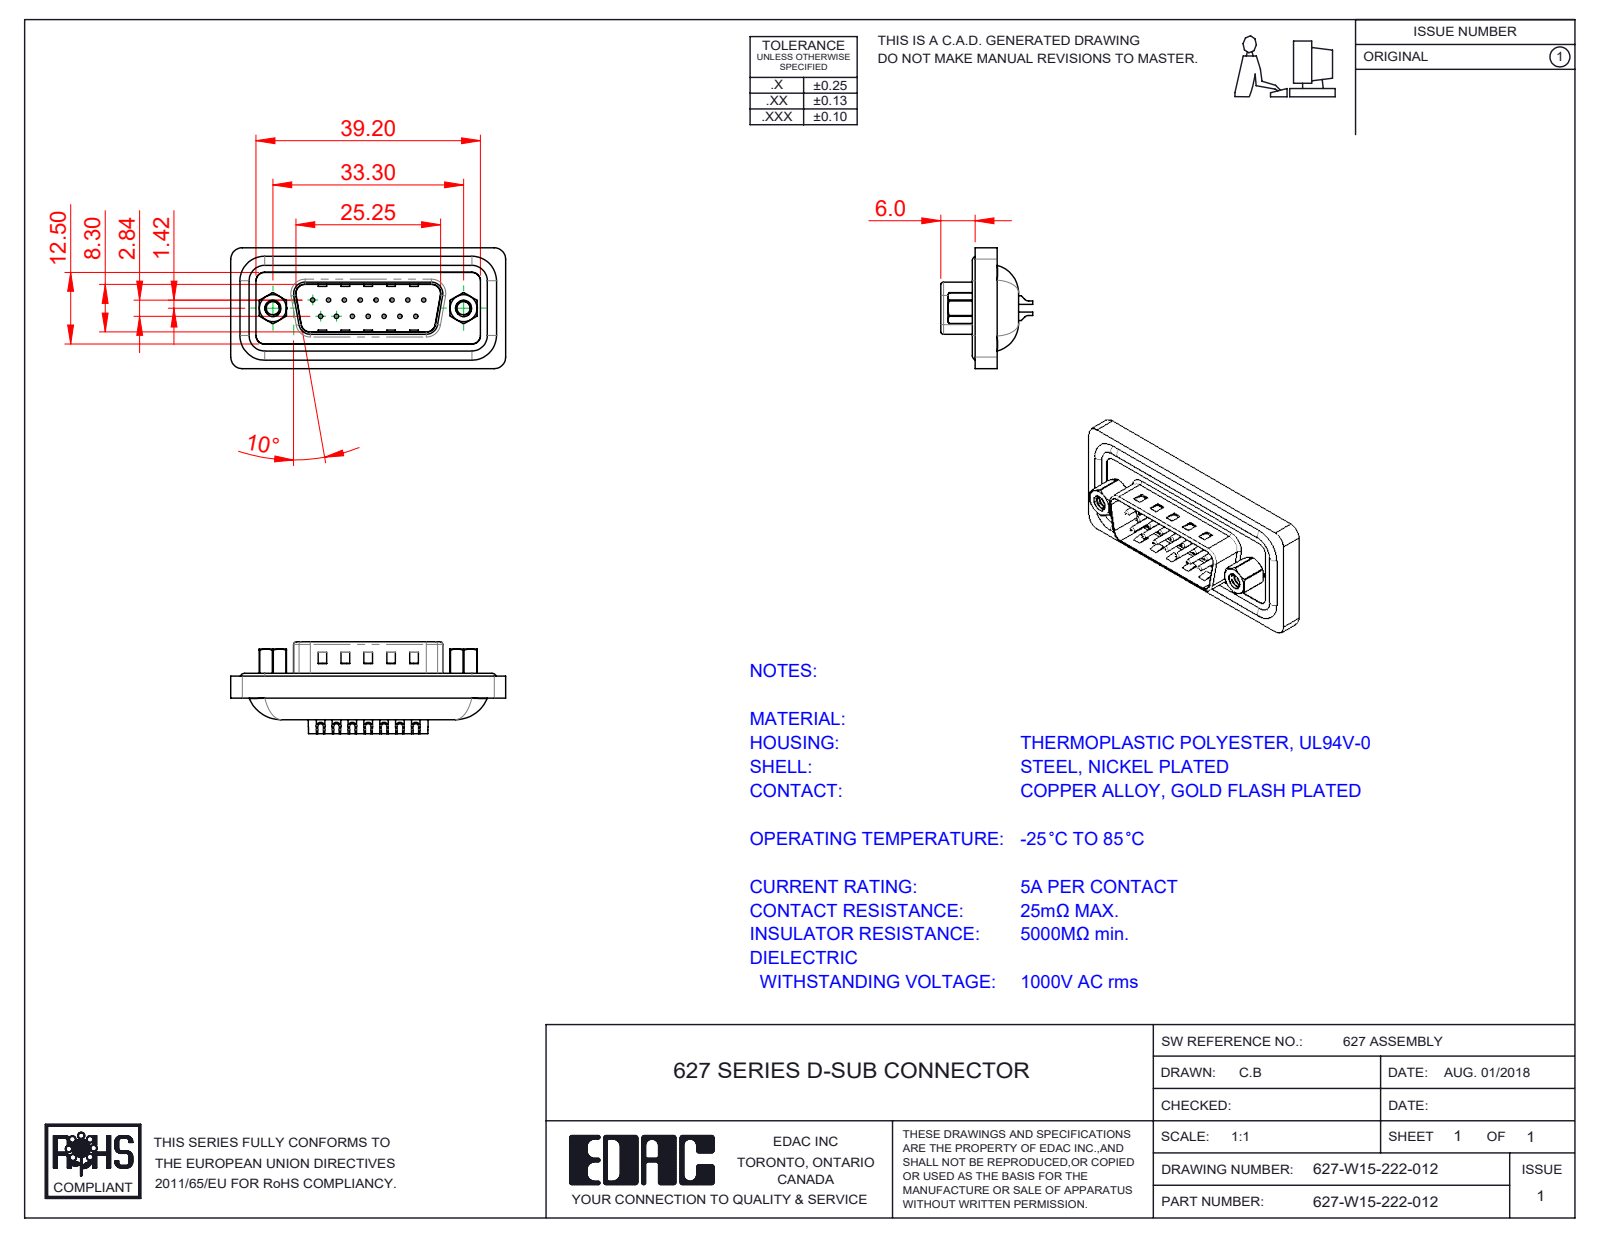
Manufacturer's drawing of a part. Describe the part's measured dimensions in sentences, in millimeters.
The part is named "627W 4-40 Threaded Rivet; 627W Housing_15 Contacts; 627W Contact Row 2_22; 627W 4-40 Hex Standoff (+4 more)". Its 3-D file was written by "SolidWorks 2023 (CONFIG_CONTROL_DESIGN)". It is 23 solids with 1069 faces: 308 planar, 486 cylindrical and 275 other. Overall it measures 48 by 21.1 by 16.25 millimeters. Its volume is 5 759 cubic millimeters and its surface area 8 374 square millimeters. Round holes: 15 of diameter 0.75, 15 of diameter 1, 15 of diameter 1.5, 15 of diameter 1.6, 15 of diameter 2, 2 of diameter 2.26, 2 of diameter 2.29, 2 of diameter 4, 2 of diameter 4.8, 2 of diameter 5. Round bosses or shafts: 7 of diameter 1.5, 4 of diameter 1.6, 2 of diameter 4.9, 2 of diameter 2.79. Partial cylindrical surfaces (rounded edges, fillets, slot ends): 16 of radius 2, 14 of radius 1.5, 8 of radius 0.5, 6 of radius 2.7, 4 of radius 0.9, 4 of radius 1.6, 4 of radius 4.3, 2 of radius 0.4. The main face-to-face distances are 0.4, 0.75, 1.1, 2.75, 3.75, 0.5, 4.6, 1.6, 1, 1.85. The hole center spacings are 3.16, 2.77, 5.54, 8.31, 5.03, 5.04, 7.48, 7.49.
